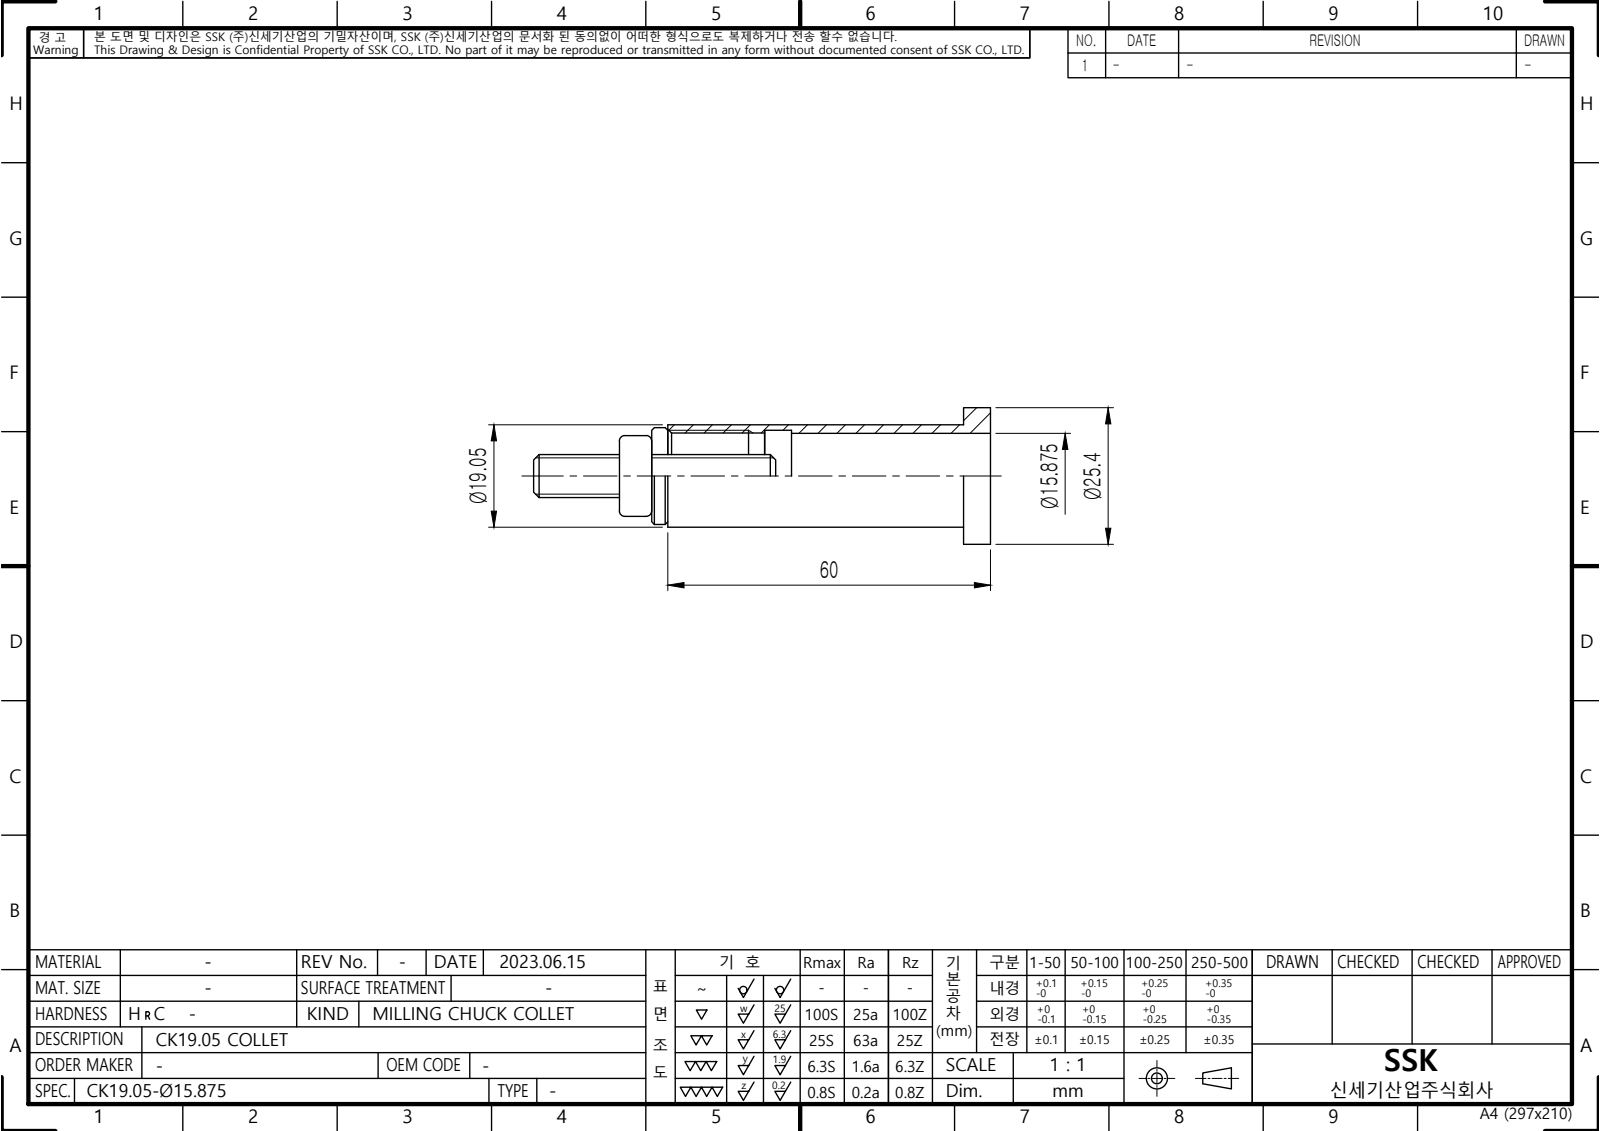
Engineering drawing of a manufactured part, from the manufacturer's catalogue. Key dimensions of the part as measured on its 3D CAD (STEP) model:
Part name (STEP PRODUCT): LO-CK19.05-15.875
STEP written by: Autodesk Inventor 2022 (AUTOMOTIVE_DESIGN)
Units: millimetres
Bodies: 1 solid, 10 faces (5 planar, 5 cylindrical, 0 other)
Overall size (bounding box): 60 × 25.4 × 25.4
Volume: 6 170 mm³ · Surface area: 7 377 mm²
Round holes (diameter × count): ⌀15.88 ×1, ⌀15.92 ×1, ⌀17 ×1
Round bosses / shafts (diameter × count): ⌀25.4 ×1, ⌀19.05 ×1
Main face-to-face distances: 5, 55, 60, 37, 23, 32, 18, 42
